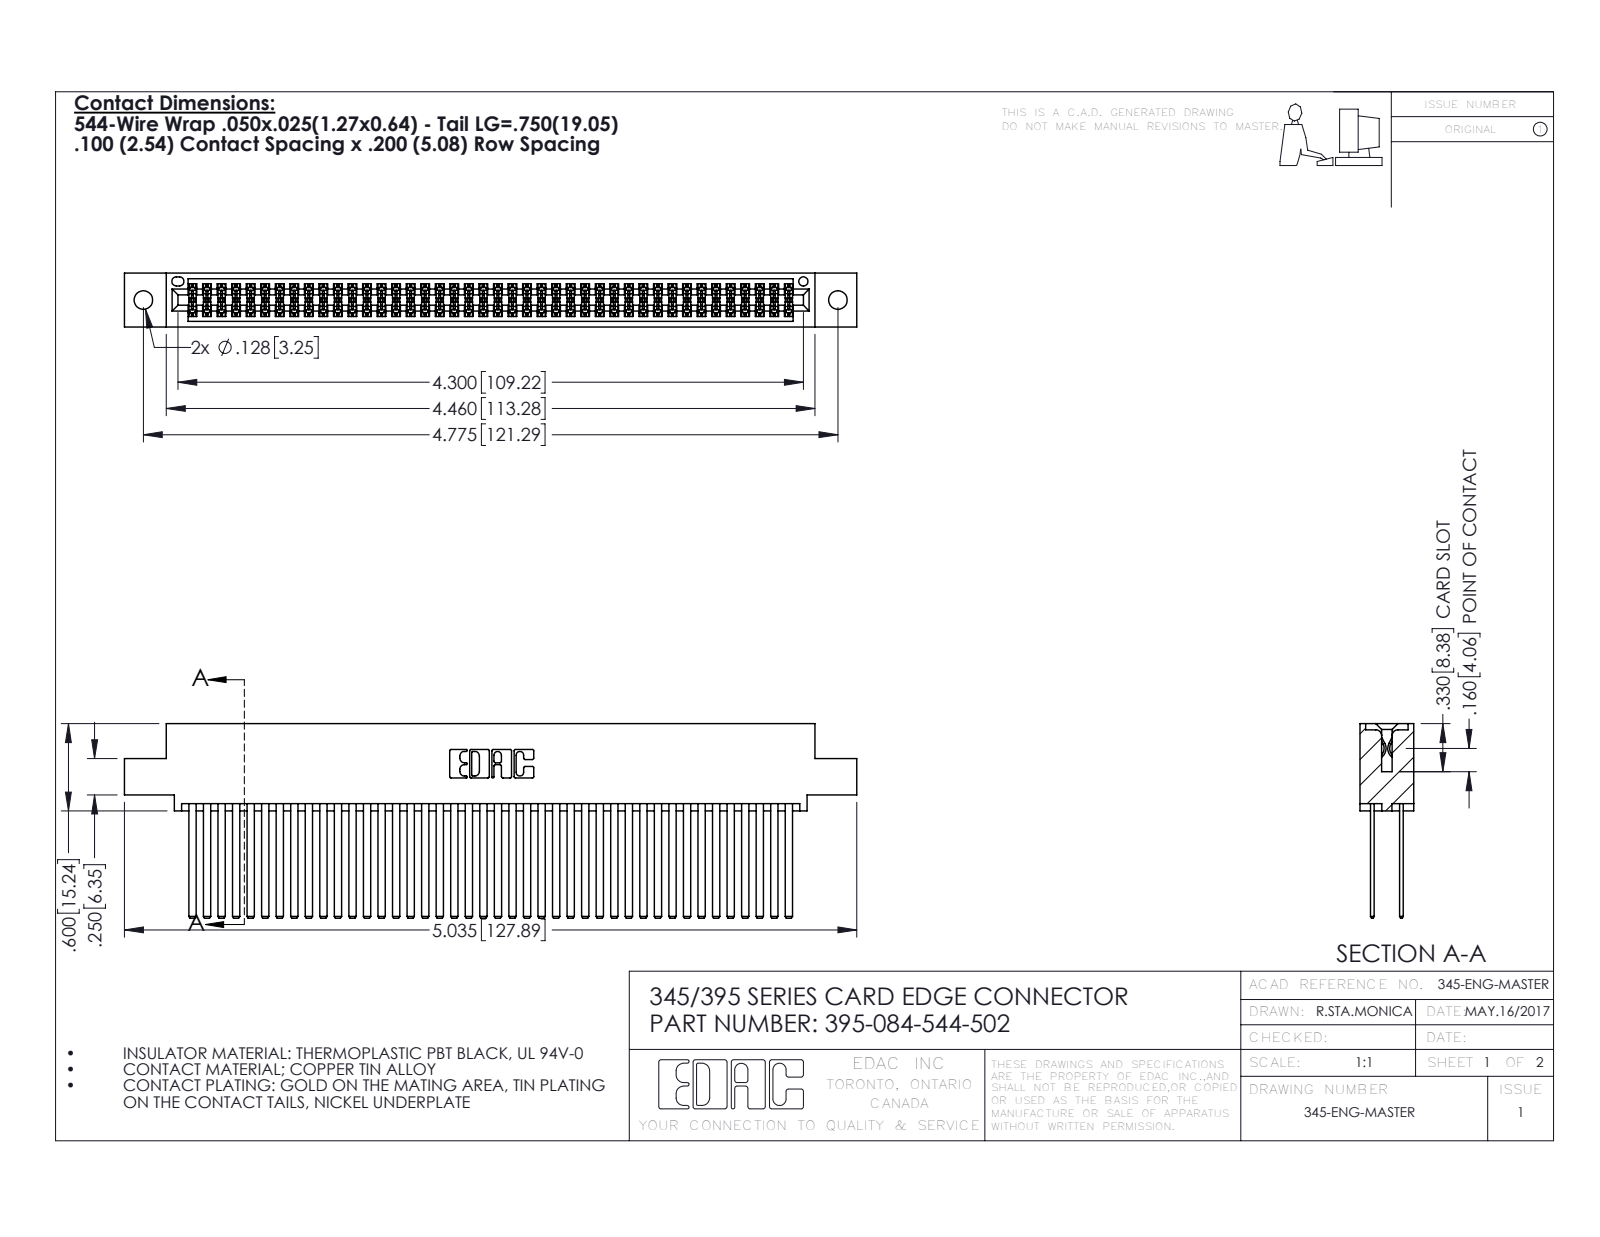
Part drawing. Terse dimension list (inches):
name: 345-292-001_345-293-144; 345 Part_0.110 Offset - 0.128 Dia; 395-084-544-502
written by: SolidWorks 2016 (CONFIG_CONTROL_DESIGN)
unit: in
bodies: 85 solids, 3826 faces (2520 planar, 1306 cylindrical, 0 other)
size: 5.035 × 1.337 × 0.37
volume: 0.823 in³; area: 35.98 in²
holes: 2× ⌀0.128, 1× ⌀0.064
rounds: 126× R0.006, 22× R0.01, 6× R0.007, 6× R0.031, 3× R0.026, 2× R0.014, 2× R0.019, 2× R0.022
face distances: 0.2, 0.025, 0.072, 0.098, 0.272, 0.298, 0.225, 0.175, 0.37, 0.05
hole spacings: 0.27, 4.539, 4.775
